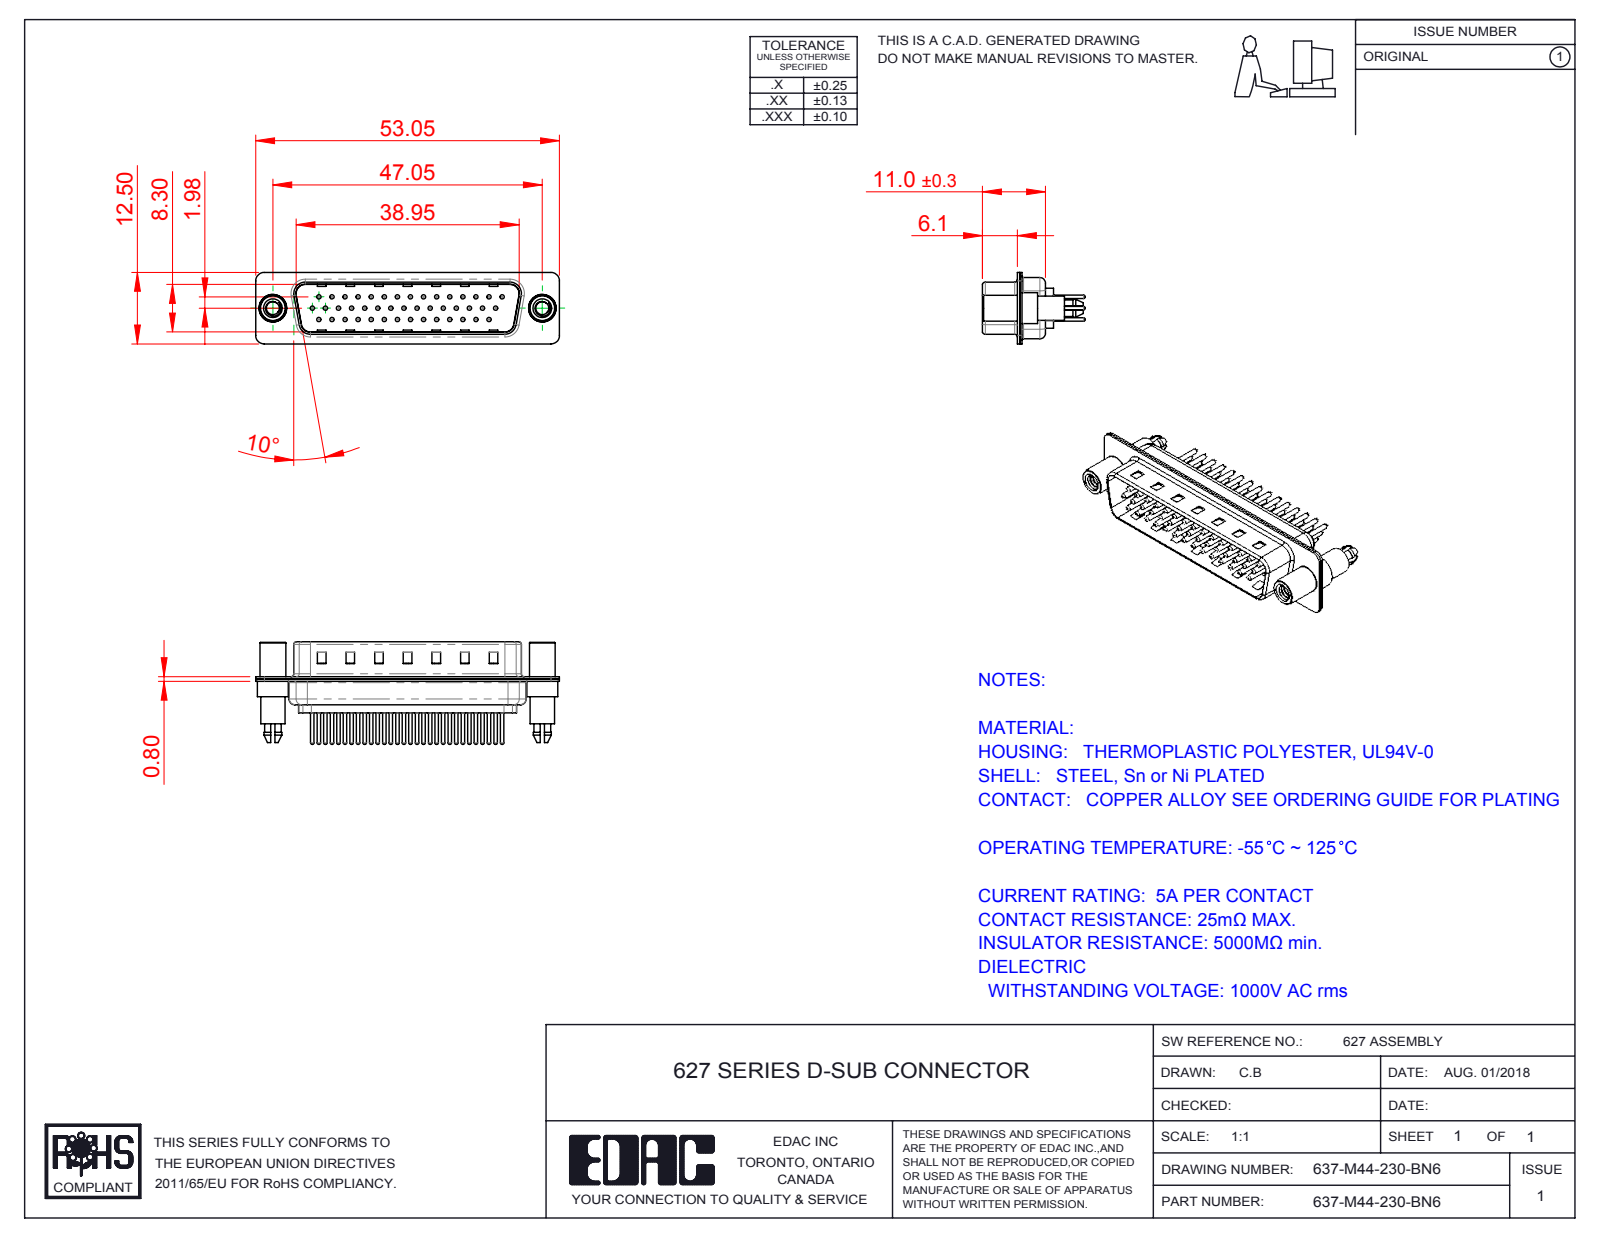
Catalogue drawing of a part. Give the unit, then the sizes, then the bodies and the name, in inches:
Units: inches
Overall size (bounding box): 2.089 × 0.705 × 0.492
Round holes (diameter × count): ⌀0.03 ×44, ⌀0.063 ×44, ⌀0.079 ×44, ⌀0.089 ×2, ⌀0.157 ×2, ⌀0.189 ×2
Round bosses / shafts (diameter × count): ⌀0.059 ×44, ⌀0.024 ×44, ⌀0.079 ×3, ⌀0.03 ×3, ⌀0.213 ×2, ⌀0.193 ×2, ⌀0.177 ×2, ⌀0.167 ×2
Partial cylindrical surfaces — rounded edges, fillets, slot ends (radius × count): R0.059 ×18, R0.079 ×12, R0.063 ×10, R0.02 ×8, R0.01 ×4, R0.024 ×4, R0.026 ×4, R0.035 ×4
Main face-to-face distances: 0.016, 0.031, 0.374, 0.358, 0.343, 0.39, 0.03, 0.248, 0.043, 0.014
Hole centre spacings: 0.09, 0.156, 0.09, 0.18, 0.324, 0.27, 0.45, 0.59
Volume: 0.193 in³ · Surface area: 13.87 in²
Bodies: 49 solids, 2088 faces (517 planar, 789 cylindrical, 782 other)
Part name (STEP PRODUCT): 637M Contact Row 1_30; 637M Contact Row 2_30; 637M Shell Rear_44 Contacts; 637M Housing_44 Contacts (+4 more)
STEP written by: SolidWorks 2016 (CONFIG_CONTROL_DESIGN)
